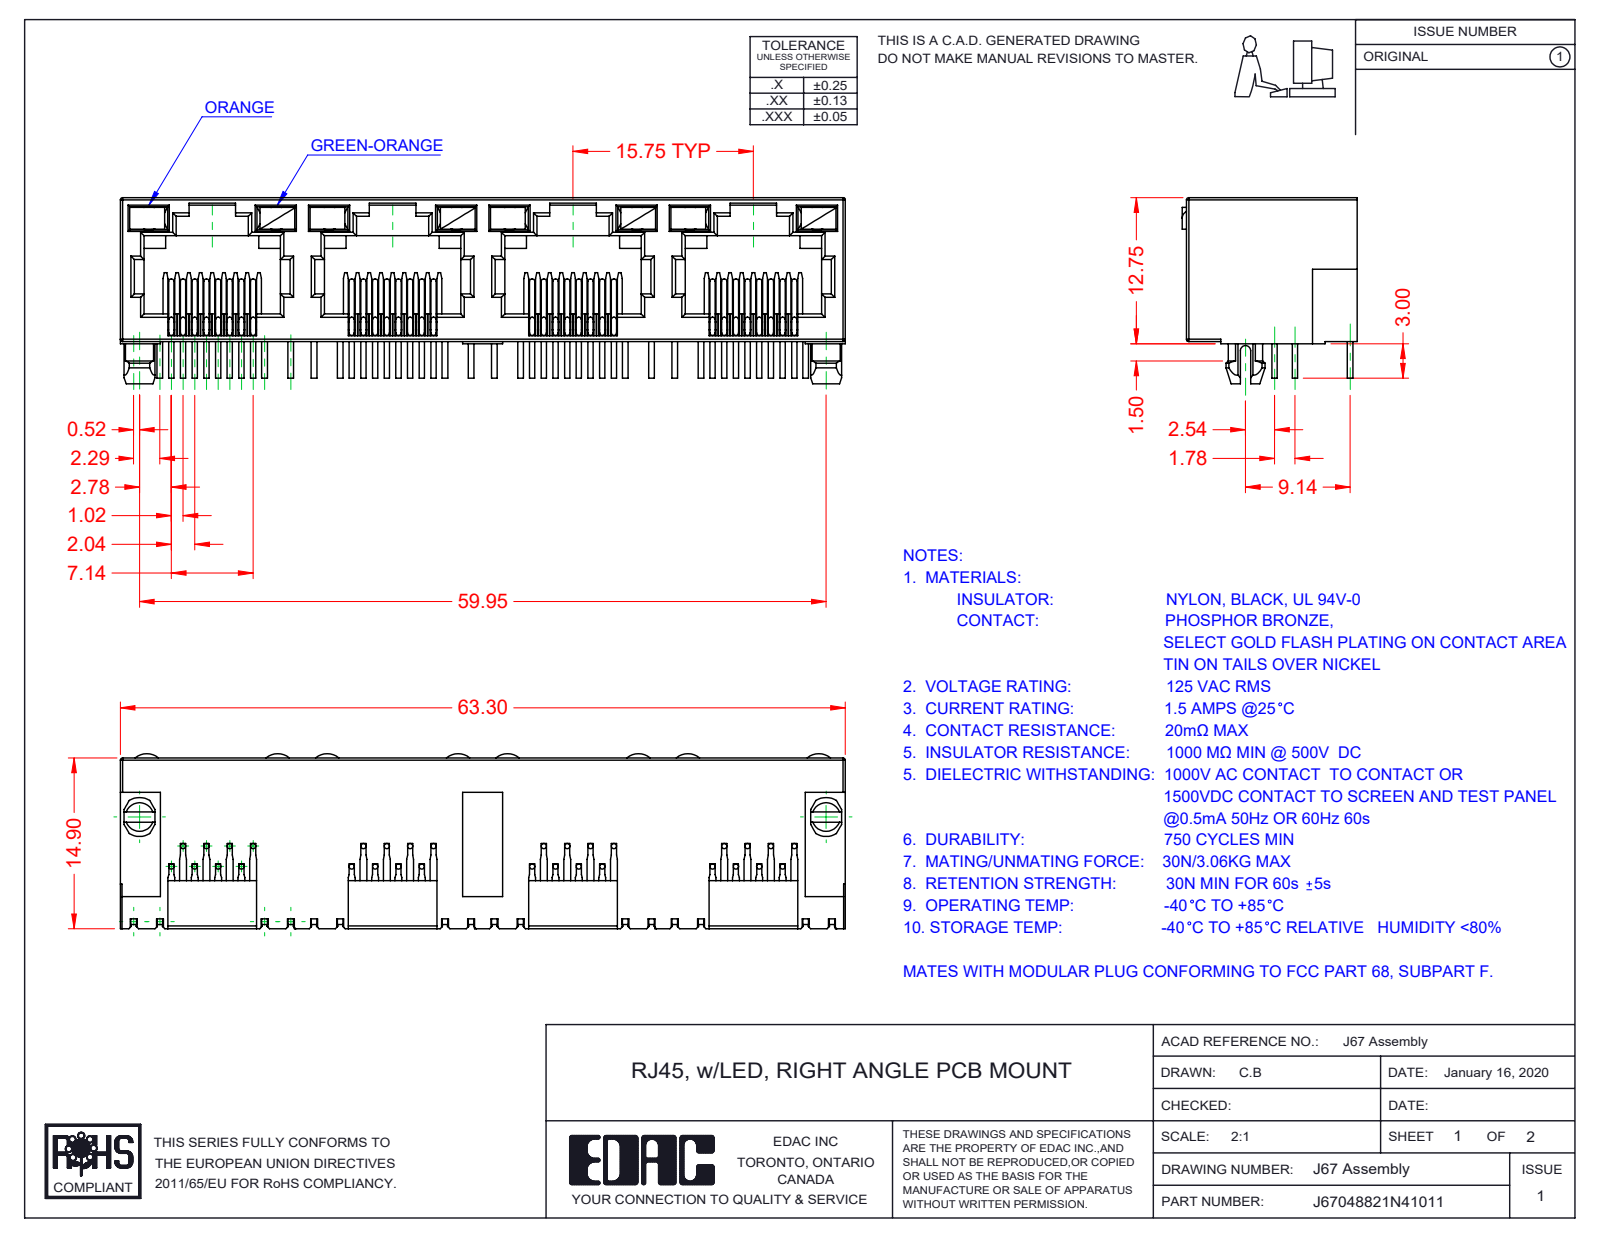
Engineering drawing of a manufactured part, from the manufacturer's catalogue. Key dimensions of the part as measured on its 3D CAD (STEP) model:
Part name (STEP PRODUCT): 67 Contacts; J67048822N47011; 67 LED LH_4-Orange; 67 LED RH_7-Green-Orange (+1 more)
STEP written by: SolidWorks 2016 (CONFIG_CONTROL_DESIGN)
Units: millimetres
Bodies: 41 solids, 2473 faces (1781 planar, 484 cylindrical, 208 other)
Overall size (bounding box): 63.3 × 16.25 × 15.28
Volume: 5 159 mm³ · Surface area: 11 573 mm²
Round bosses / shafts (diameter × count): ⌀0.46 ×96
Partial cylindrical surfaces — rounded edges, fillets, slot ends (radius × count): R0.2 ×66, R0.3 ×29, R0.45 ×9, R1.55 ×8, R1.5 ×2, R1.7 ×2, R0.35 ×1, R1 ×1
Main face-to-face distances: 0.5, 12.55, 1.89, 0.89, 10, 15.75, 1, 1.39, 11, 11.89
